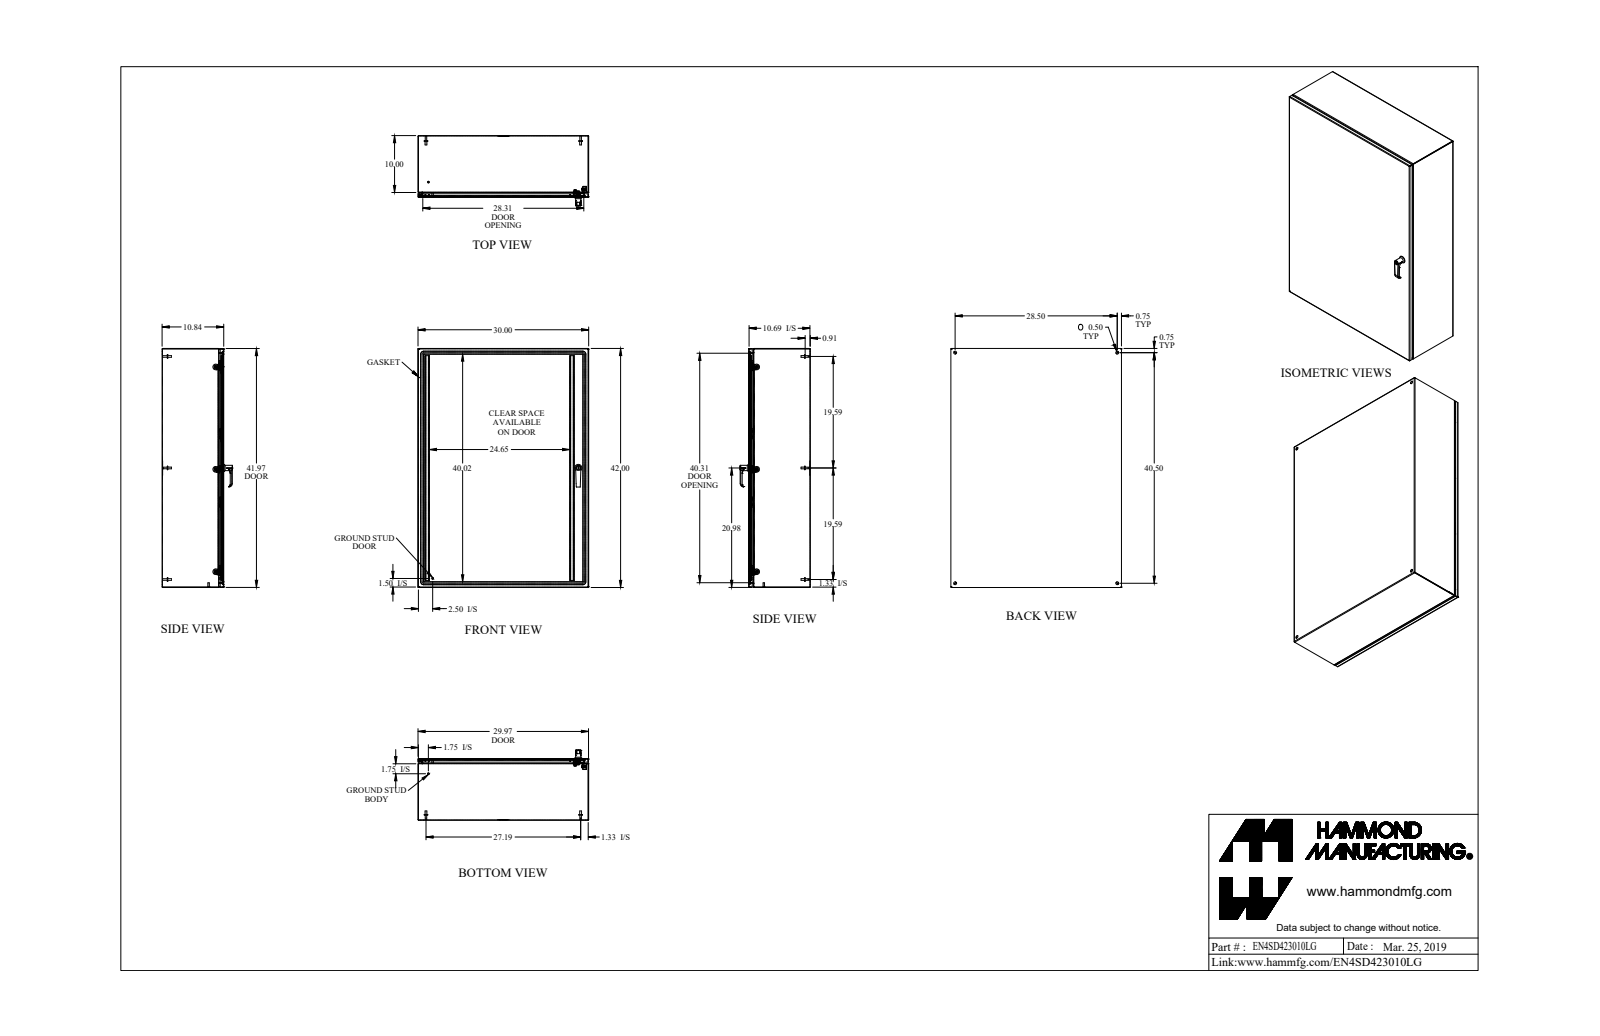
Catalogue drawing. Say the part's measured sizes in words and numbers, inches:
The part is named "EN4SD423010LG". Its 3-D file was written by "SolidWorks 2019 (AUTOMOTIVE_DESIGN)". It is 53 solids with 1457 faces: 632 planar, 538 cylindrical and 287 other. Overall it measures 42 by 30 by 12.367 inches. Its volume is 333.5 cubic inches and its surface area 9 246 square inches. Round holes: 6 of diameter 0.176, 4 of diameter 0.5, 3 of diameter 0.196, 3 of diameter 0.25, 3 of diameter 0.265, 3 of diameter 0.413, 2 of diameter 0.256, 2 of diameter 0.313, 2 of diameter 0.394, 1 of diameter 0.172, 1 of diameter 0.24, 1 of diameter 0.242. Round bosses or shafts: 7 of diameter 0.25, 6 of diameter 0.375, 6 of diameter 0.313, 6 of diameter 0.27, 6 of diameter 0.156, 4 of diameter 0.625, 3 of diameter 1, 2 of diameter 0.63. Partial cylindrical surfaces (rounded edges, fillets, slot ends): 20 of radius 0.036, 20 of radius 0.108, 15 of radius 0.03, 12 of radius 0.043, 12 of radius 0.081, 8 of radius 0.006, 8 of radius 0.04, 8 of radius 0.062. The main face-to-face distances are 0.072, 10.765, 10.693, 10.837, 29.928, 41.928, 29.856, 30, 41.856, 42. The hole center spacings are 2.507, 18, 27.52, 28.5, 35.969, 38.25, 40.5, 47.055.
